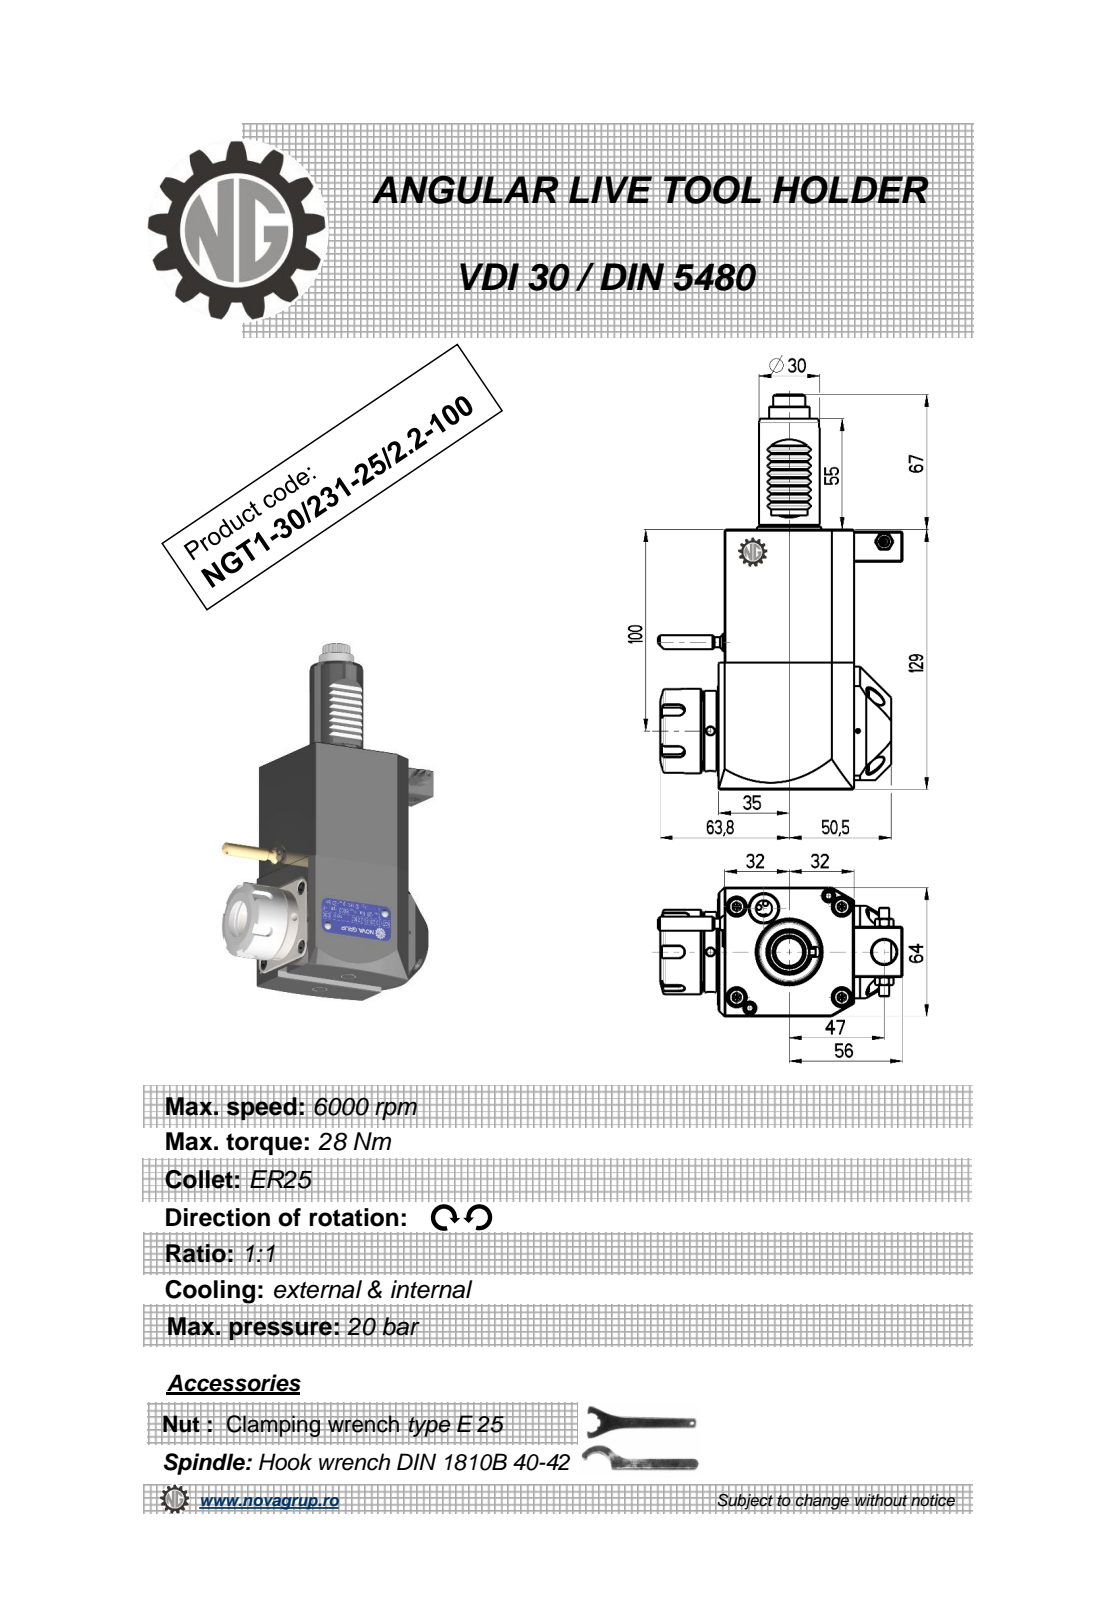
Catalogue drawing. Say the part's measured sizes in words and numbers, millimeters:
The part is named "NGT1_30_231_25_2_2_100". Its 3-D file was written by "PRO/ENGINEER BY PARAMETRIC TECHNOLOGY CORPORATION, 2010280 (CONFIG_CONTROL_DESIGN)". It is 1 solid with 498 faces: 184 planar, 157 cylindrical and 157 other. Overall it measures 196 by 120.88 by 65.6 millimeters. Its volume is 643 488 cubic millimeters and its surface area 58 785 square millimeters. Round holes: 2 of diameter 4, 1 of diameter 2.5, 1 of diameter 3, 1 of diameter 4.2, 1 of diameter 9.5, 1 of diameter 12, 1 of diameter 20.3. Round bosses or shafts: 2 of diameter 8.96, 2 of diameter 5, 1 of diameter 42, 1 of diameter 40, 1 of diameter 33, 1 of diameter 30, 1 of diameter 20, 1 of diameter 7. Partial cylindrical surfaces (rounded edges, fillets, slot ends): 36 of radius 1.98, 12 of radius 0.26, 8 of radius 0.3, 5 of radius 3, 2 of radius 160, 1 of radius 7.08, 1 of radius 7.92, 1 of radius 13. The main face-to-face distances are 64, 129, 3.2, 67.2, 67, 3, 18.5, 0.5, 85.7, 85.5. The hole center spacings are 46.17, 49.52, 85.95, 91.5, 127.37.
